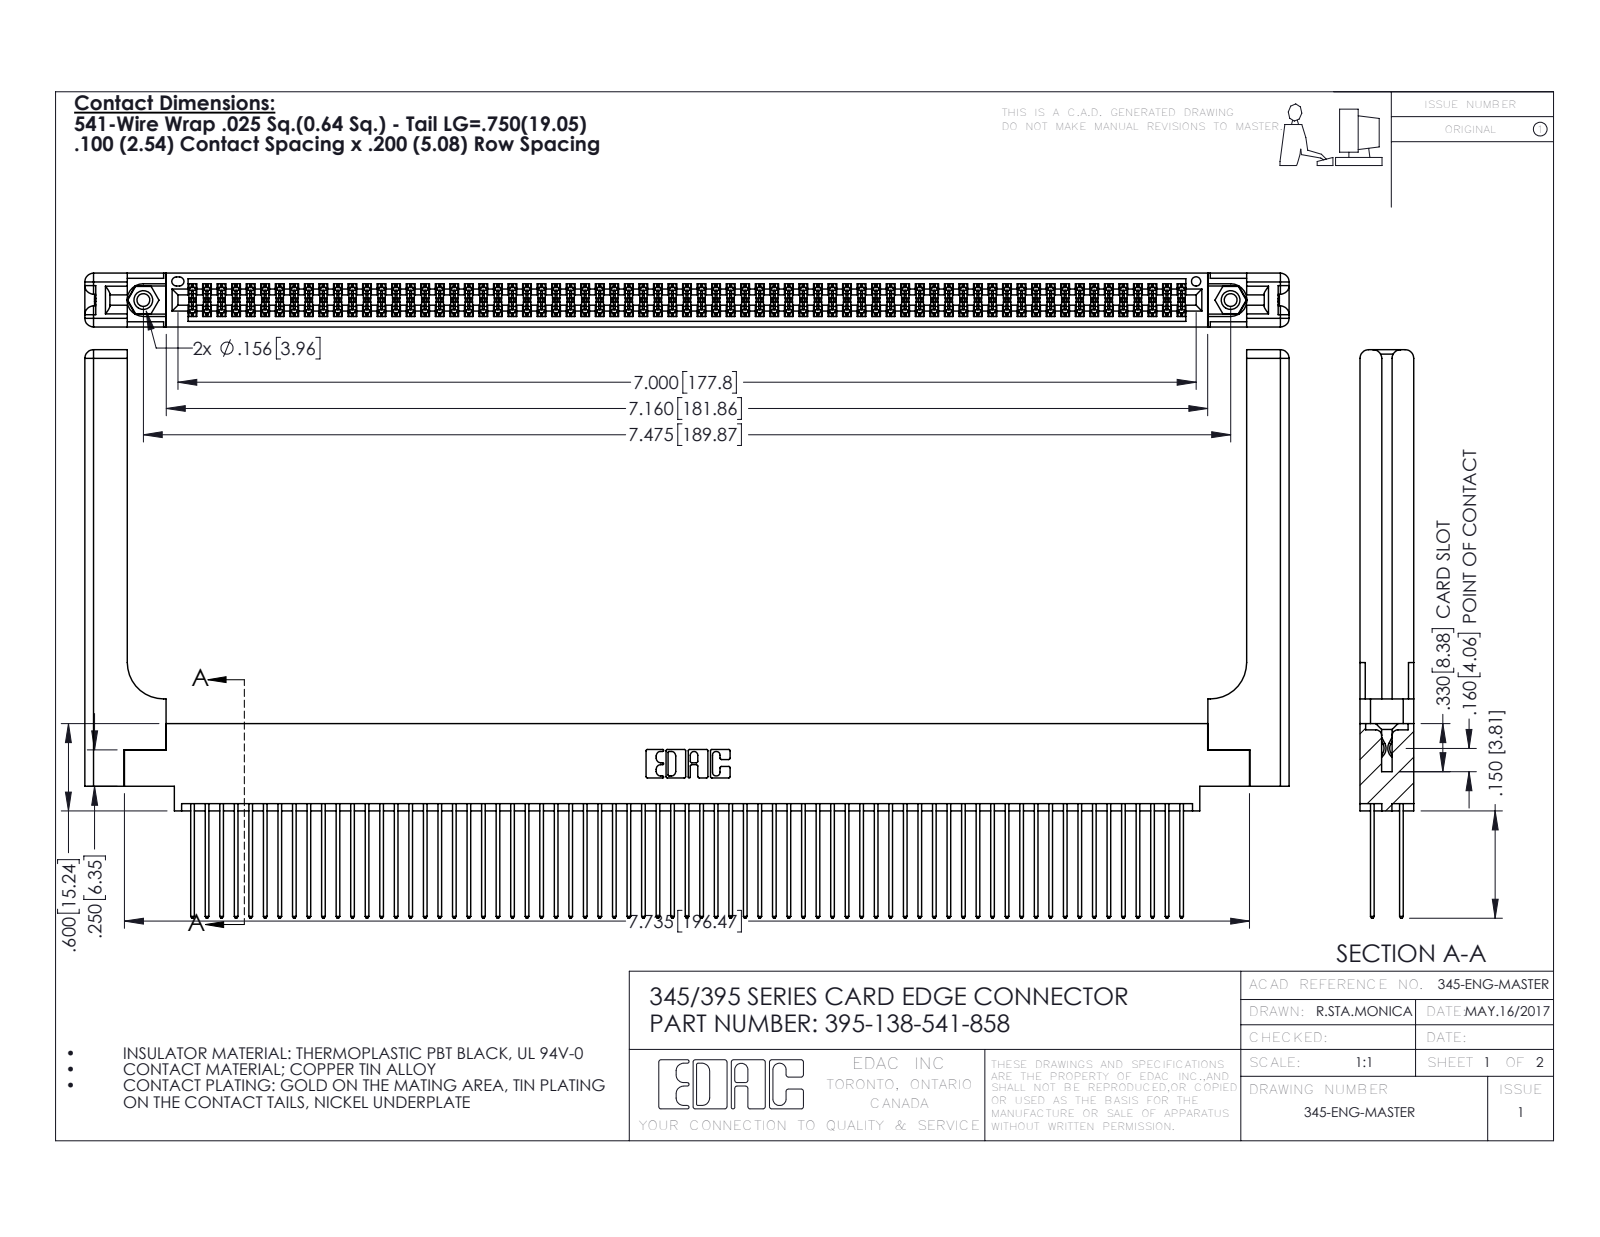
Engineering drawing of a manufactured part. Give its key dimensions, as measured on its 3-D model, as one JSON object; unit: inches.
{"part_name": "345-292-001_345-293-141; 395-138-541-858; 345-220-058_345-220-058; 345 Part_0.170 Offset - 0.156 Dia-TH (+1 more)", "step_written_by": "SolidWorks 2016 (CONFIG_CONTROL_DESIGN)", "units": "inches", "bodies": {"solids": 143, "faces": 7286, "planar": 4786, "cylindrical": 2440, "other": 60}, "overall_size": [8.279, 3.907, 0.37], "volume_in3": 1.82, "surface_area_in2": 63.57, "round_holes": [[0.089, 2], [0.125, 2], [0.156, 2], [0.064, 1]], "round_bosses_or_shafts": [[0.155, 2]], "partial_cylinders_radius": [[0.006, 207], [0.01, 138], [0.01, 22], [0.06, 16], [0.007, 6], [0.031, 6], [0.026, 3], [0.014, 2]], "face_to_face_distances": [0.072, 0.298, 0.098, 0.272, 0.025, 0.2, 0.37, 0.225, 0.175, 0.148], "hole_center_spacings": [0.27, 7.239, 7.475]}
